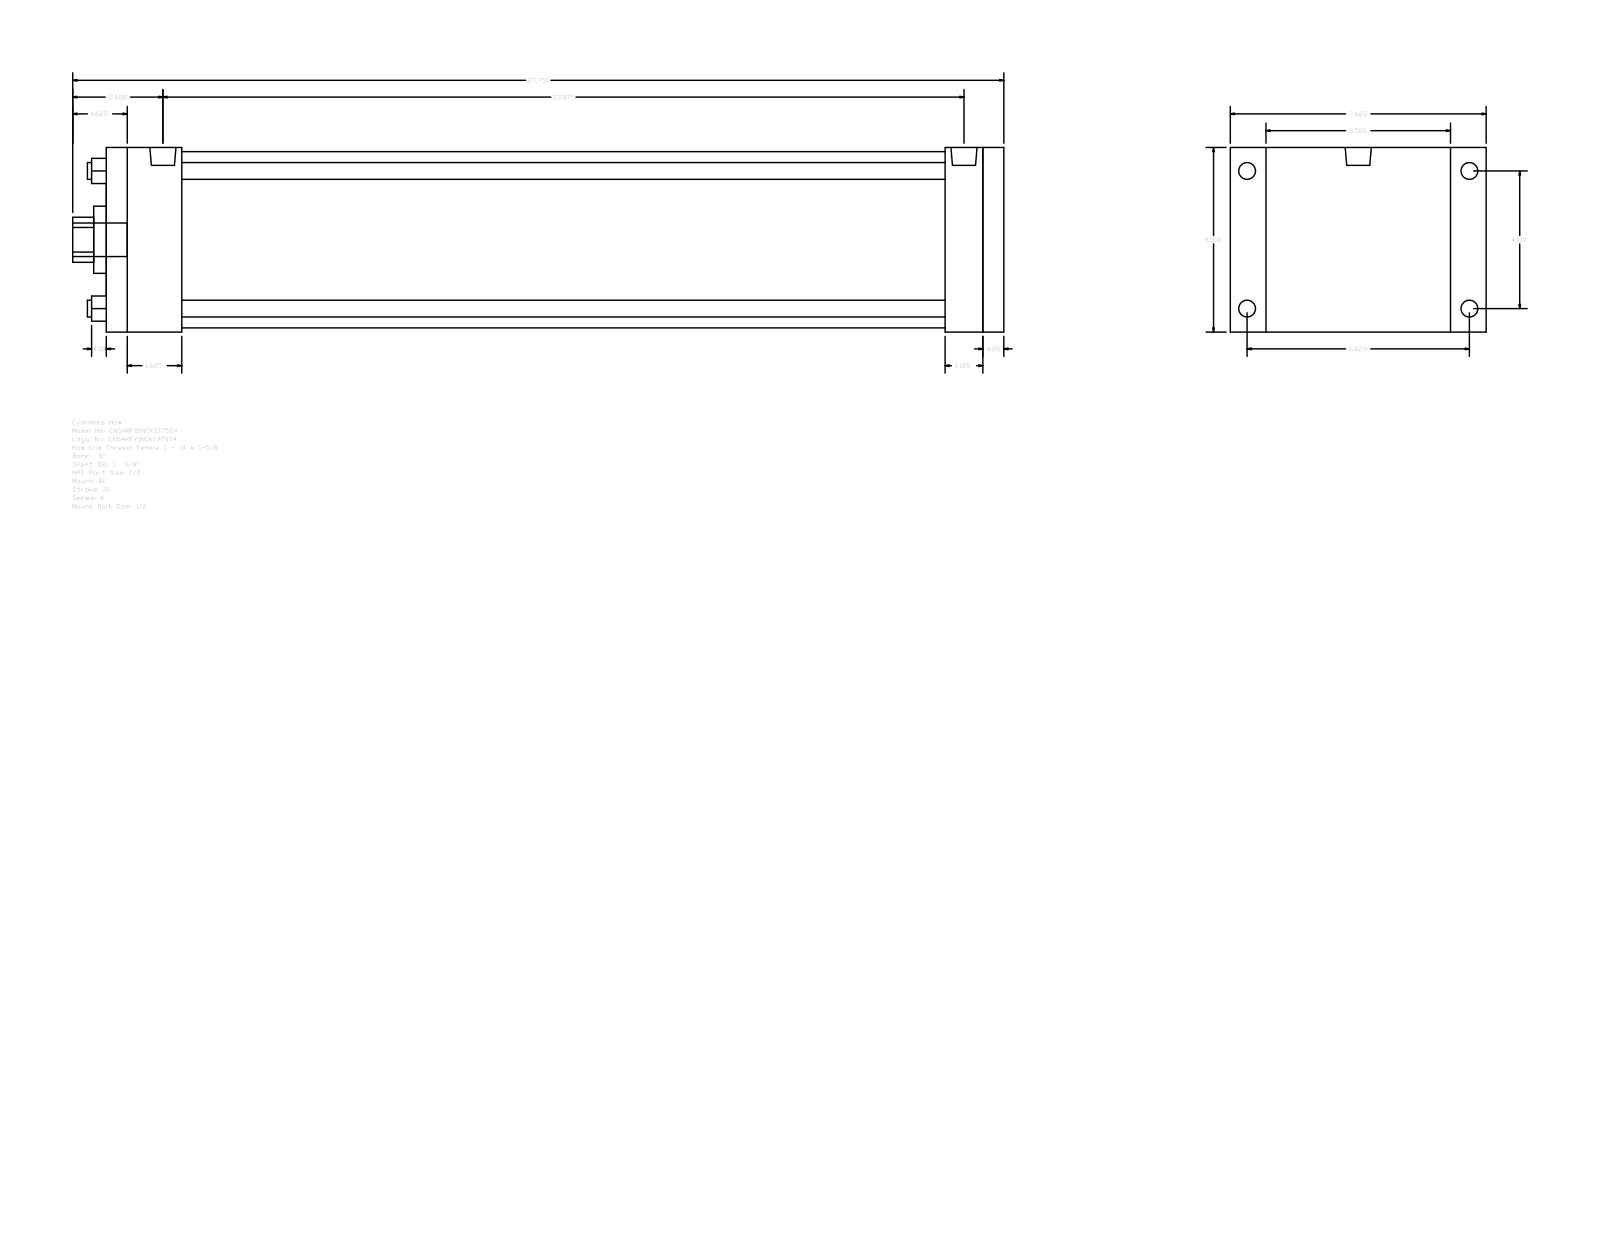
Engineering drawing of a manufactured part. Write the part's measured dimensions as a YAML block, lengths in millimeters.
part_name: "A_RF__0500_1.375"
step_written_by: "GSSL Pune (CONFIG_CONTROL_DESIGN)"
units: millimeters
bodies: {solids: 0, faces: 92, planar: 64, cylindrical: 28, other: 0}
overall_size: [704.85, 193.68, 139.7]
round_holes:
  - {diameter: 12.7, count: 4}
  - {diameter: 34.92, count: 1}
  - {diameter: 50.8, count: 1}
  - {diameter: 133.35, count: 1}
round_bosses_or_shafts:
  - {diameter: 12.7, count: 4}
  - {diameter: 8.73, count: 4}
  - {diameter: 19.77, count: 2}
  - {diameter: 25.4, count: 1}
partial_cylinders:
  - {radius: 17.06, count: 1}
face_to_face_distances: [139.7, 679.45, 15.87, 663.58, 28.58, 57.15, 606.43, 622.3, 635, 577.85]
hole_center_spacings: [73.64, 104.14, 147.28]
